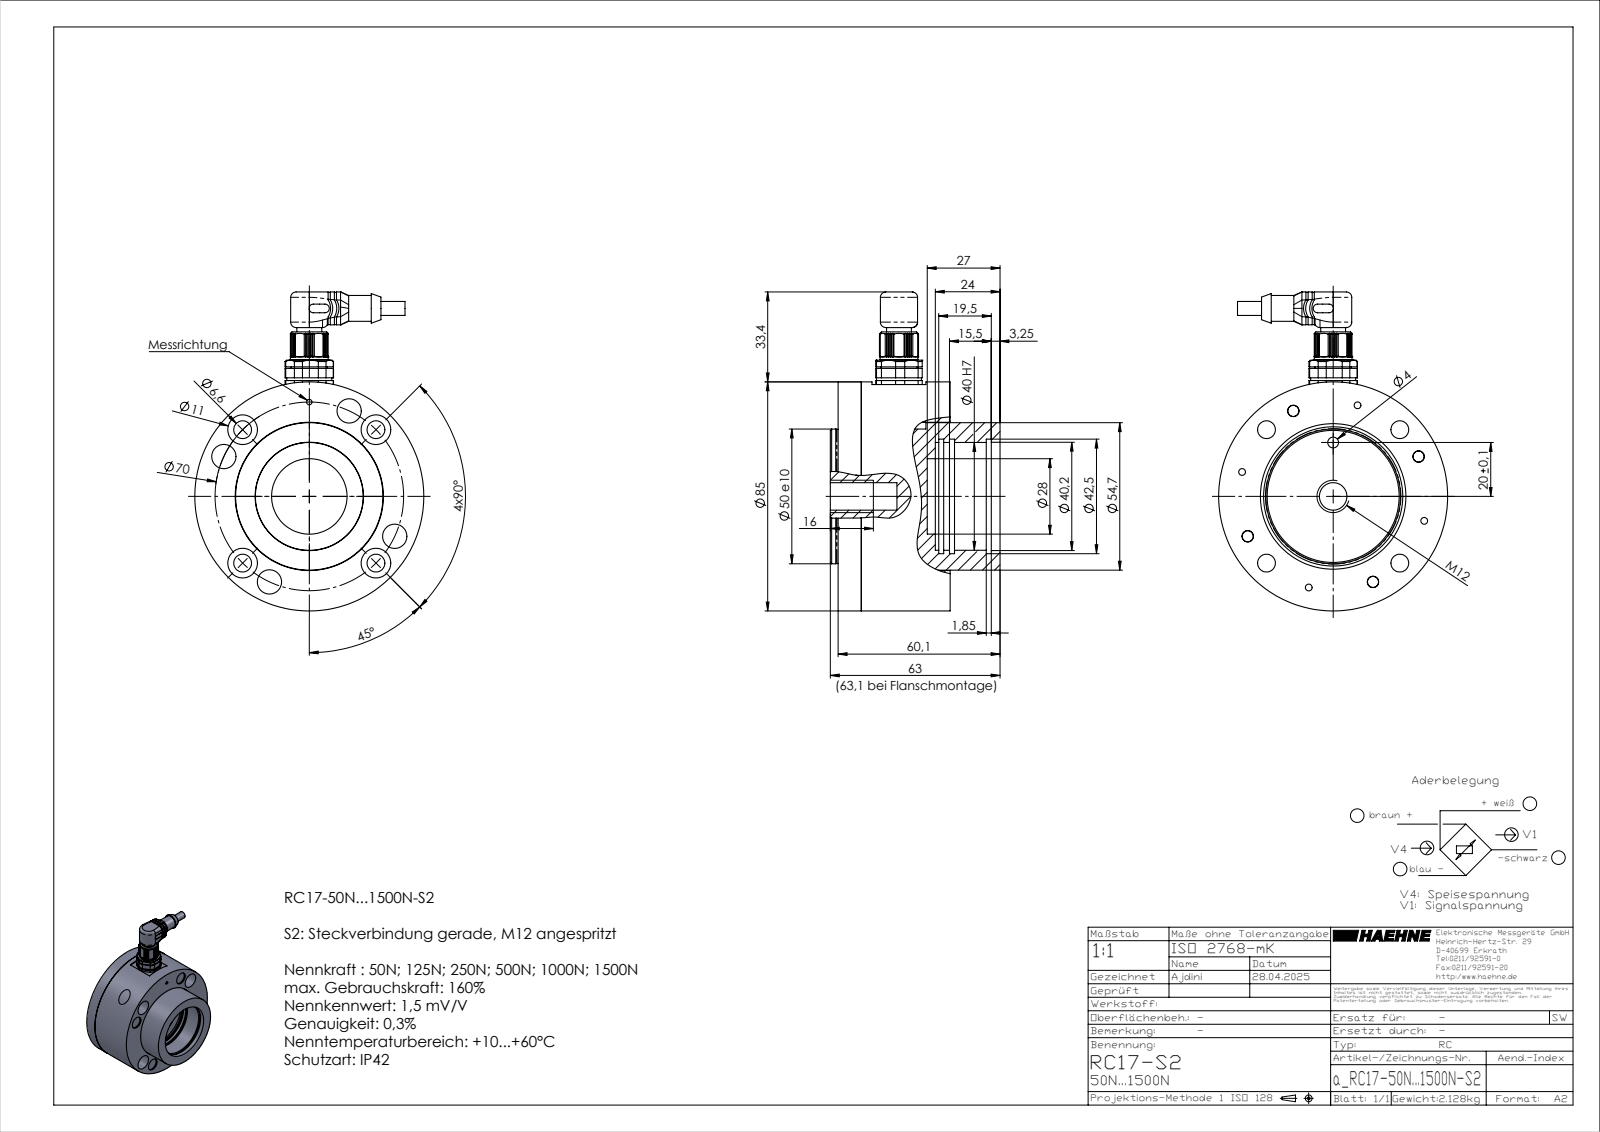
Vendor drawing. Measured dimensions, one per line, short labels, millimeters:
name: a_RC17-50N...1500N-S2 STEP; a_RC17-50N...1500N-S2; a_RC-N2 Flanschmontage Scheibe
written by: SolidWorks 2023 (AUTOMOTIVE_DESIGN)
unit: mm
bodies: 14 solids, 958 faces (521 planar, 247 cylindrical, 190 other)
size: 118.35 × 85 × 63.1
volume: 250 856 mm³; area: 77 772 mm²
holes: 5× ⌀11, 4× ⌀1.1, 4× ⌀1.15, 4× ⌀1.6, 4× ⌀1.85, 4× ⌀2.5, 4× ⌀3.4, 4× ⌀4.2, 4× ⌀5.3, 4× ⌀6.6, 4× ⌀9, 1× ⌀1.2
bosses: 4× ⌀8.5, 4× ⌀5.7, 4× ⌀5, 4× ⌀3, 4× ⌀1.8, 4× ⌀1.55, 4× ⌀1.5, 4× ⌀1
rounds: 16× R0.2, 9× R0.3, 4× R0.4, 4× R0.53, 4× R1, 4× R1.27, 4× R6, 2× R1.6
face distances: 8.6, 3, 11.6, 33, 44.6, 41.6, 11.5, 2.9, 44.5, 2
hole spacings: 35, 49.5, 2.5, 3.54, 12.16, 18.12, 23.94, 29.58
